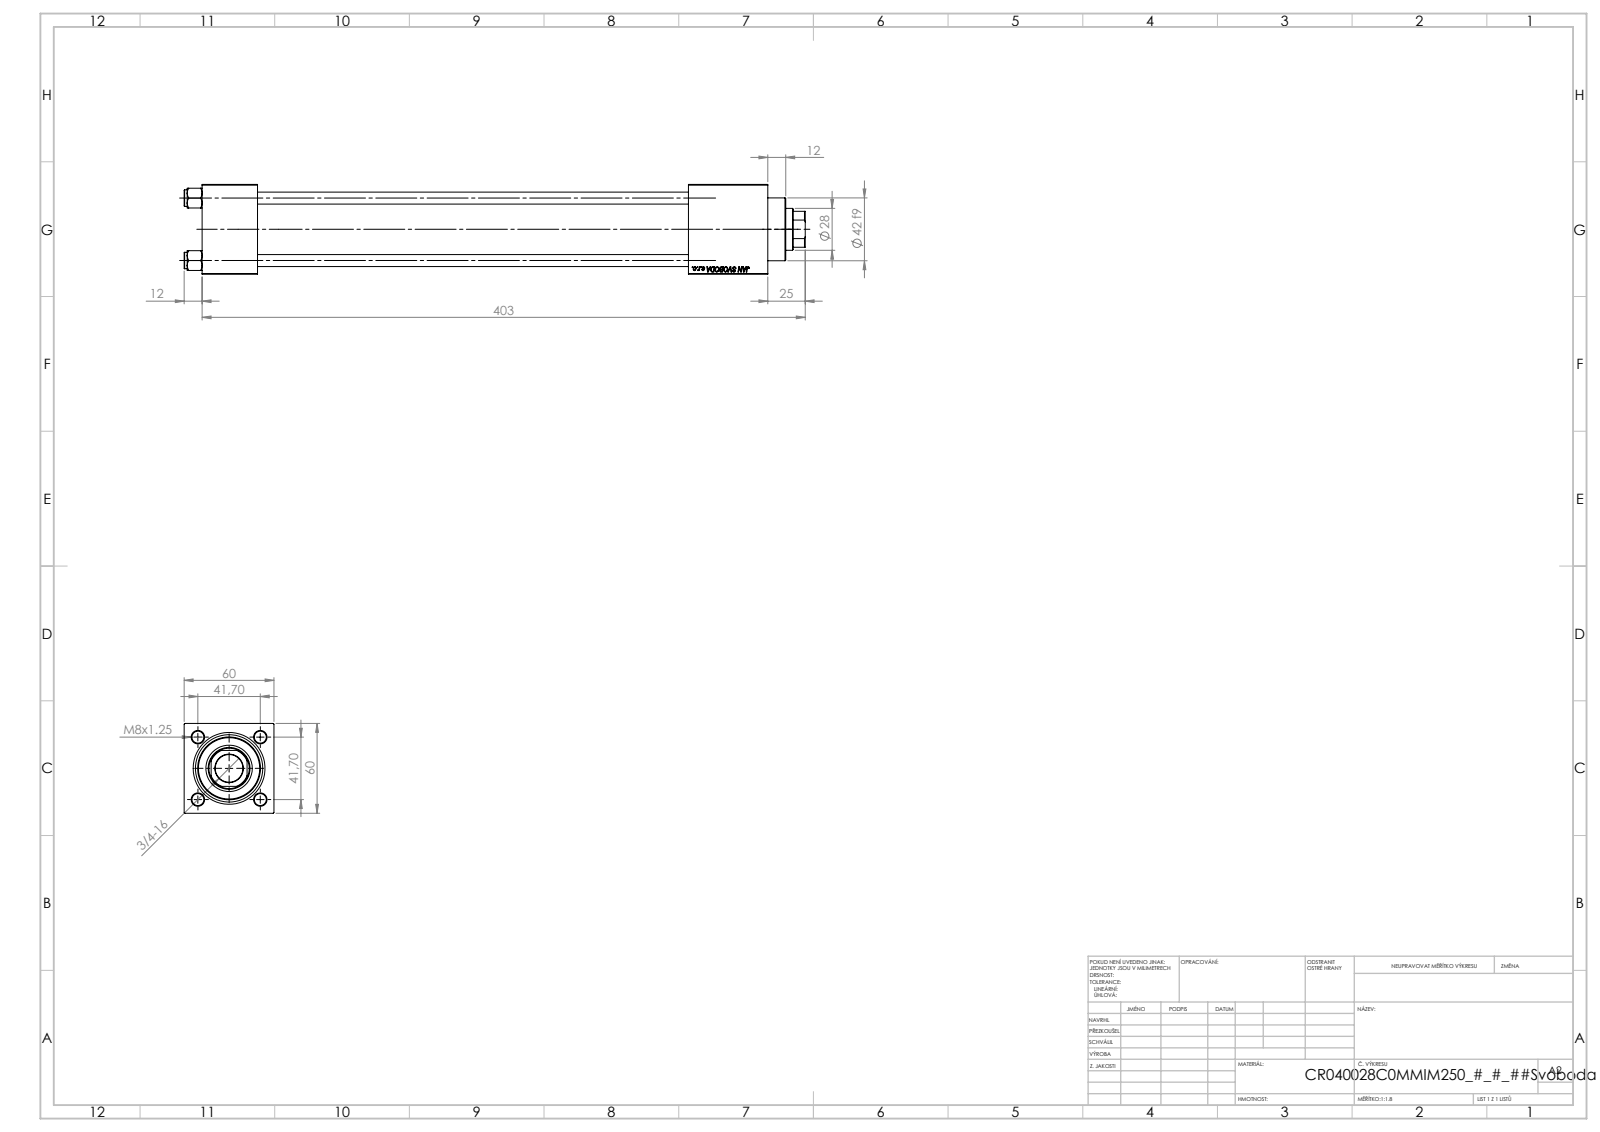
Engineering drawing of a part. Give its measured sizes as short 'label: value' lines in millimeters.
name: V215CR_VCP_C; V215CR_C_TYCINKA; V215CR_C_Body; V215_VC_A (+1 more)
written by: SolidWorks 2019 (CONFIG_CONTROL_DESIGN)
unit: mm
bodies: 11 solids, 1148 faces (526 planar, 86 cylindrical, 536 other)
size: 415 × 60 × 60
volume: 705 567 mm³; area: 216 841 mm²
holes: 4× ⌀8, 2× ⌀7, 2× ⌀16.66, 2× ⌀24, 1× ⌀18.5, 1× ⌀28, 1× ⌀31, 1× ⌀40, 1× ⌀45
bosses: 4× ⌀11, 1× ⌀46, 1× ⌀42
rounds: 1× R13.5
face distances: 60, 37, 325, 288, 349.3, 312.3, 24.3, 53, 378, 341
hole spacings: 29.49, 41.7, 58.97, 322.5
